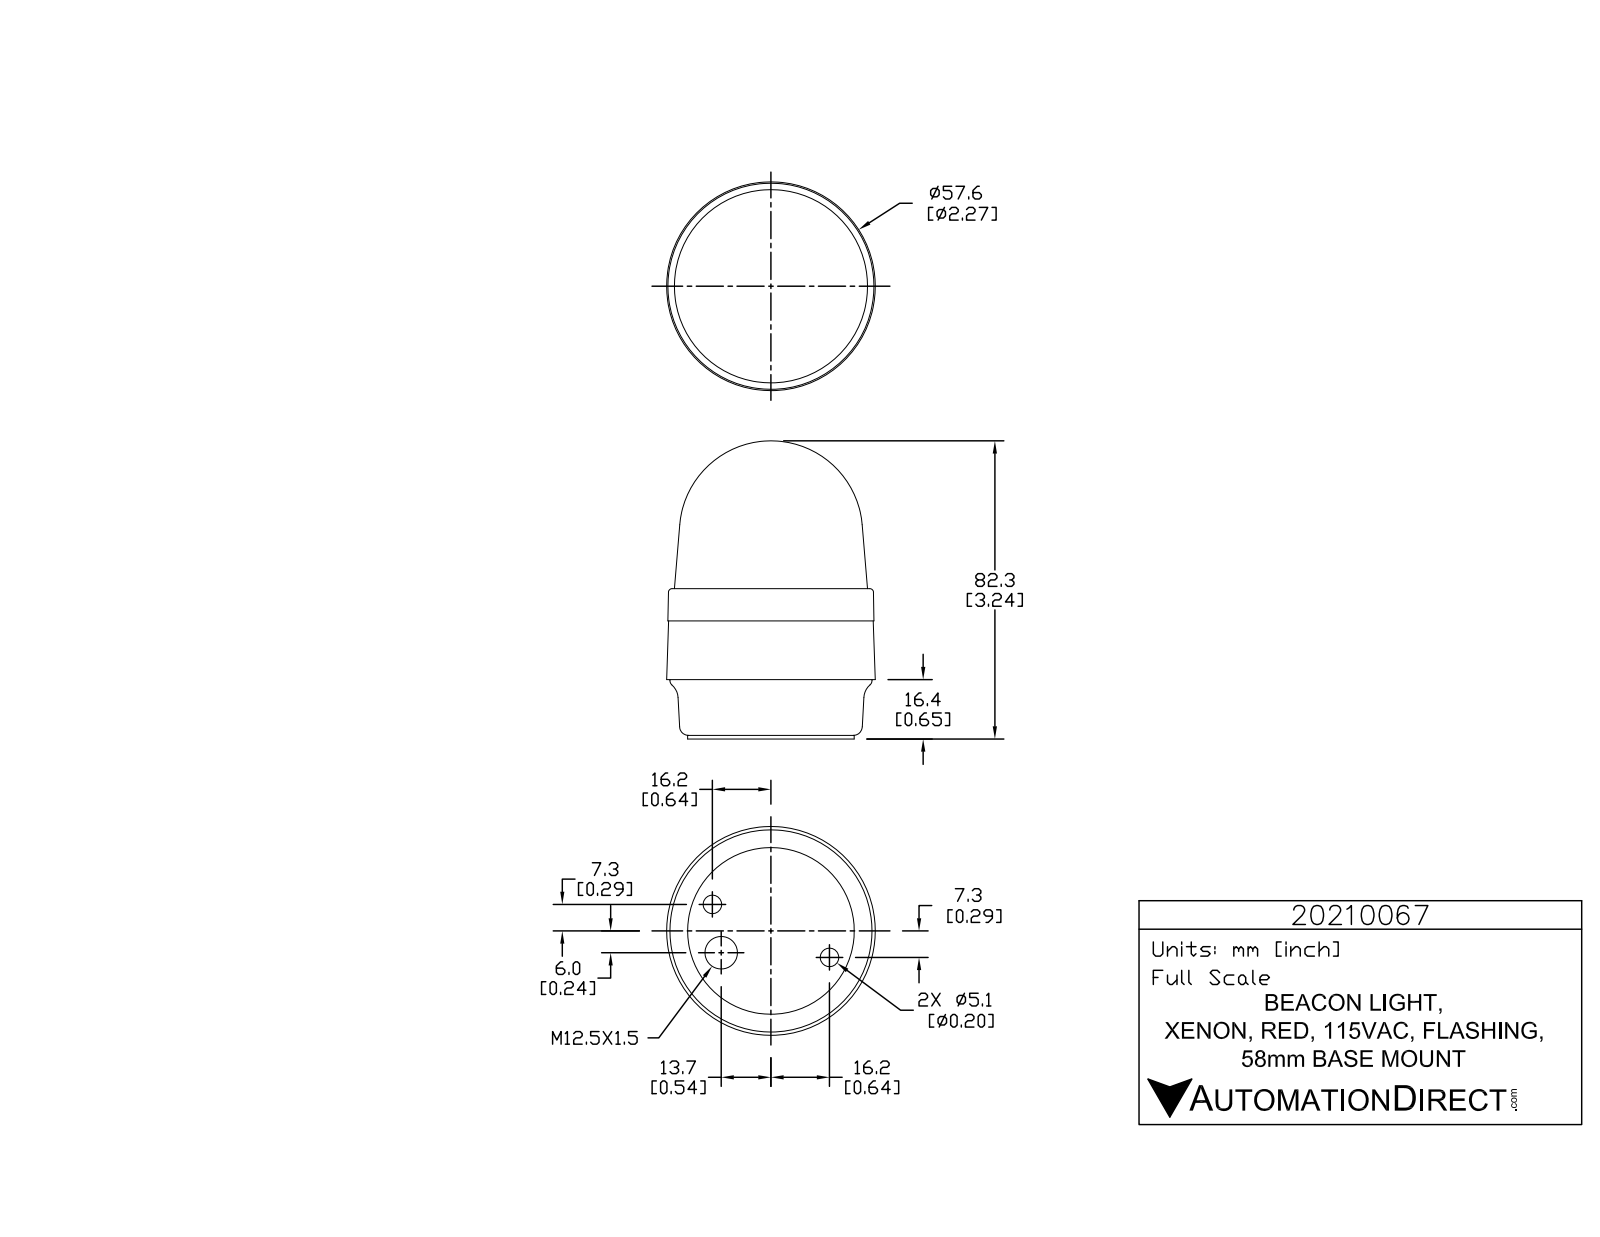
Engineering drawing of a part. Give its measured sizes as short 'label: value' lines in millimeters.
name: 20210067
written by: SolidWorks 2015 (AUTOMOTIVE_DESIGN)
unit: mm
bodies: 1 solid, 763 faces (527 planar, 145 cylindrical, 91 other)
size: 82.3 × 57.63 × 57.63
volume: 164 395 mm³; area: 16 261 mm²
holes: 3× ⌀0.99, 2× ⌀5.11, 1× ⌀9
bosses: 3× ⌀5.74, 3× ⌀1.43, 1× ⌀55.8, 1× ⌀46
rounds: 6× R0.2, 6× R0.21, 6× R0.21, 6× R3.32, 3× R0.1, 3× R0.12, 3× R0.19, 3× R0.2
face distances: 16.4, 1, 15.4, 41.5, 40.5, 25.1, 32.6, 31.6, 16.2, 8.9
hole spacings: 13.56, 29.94, 35.5
